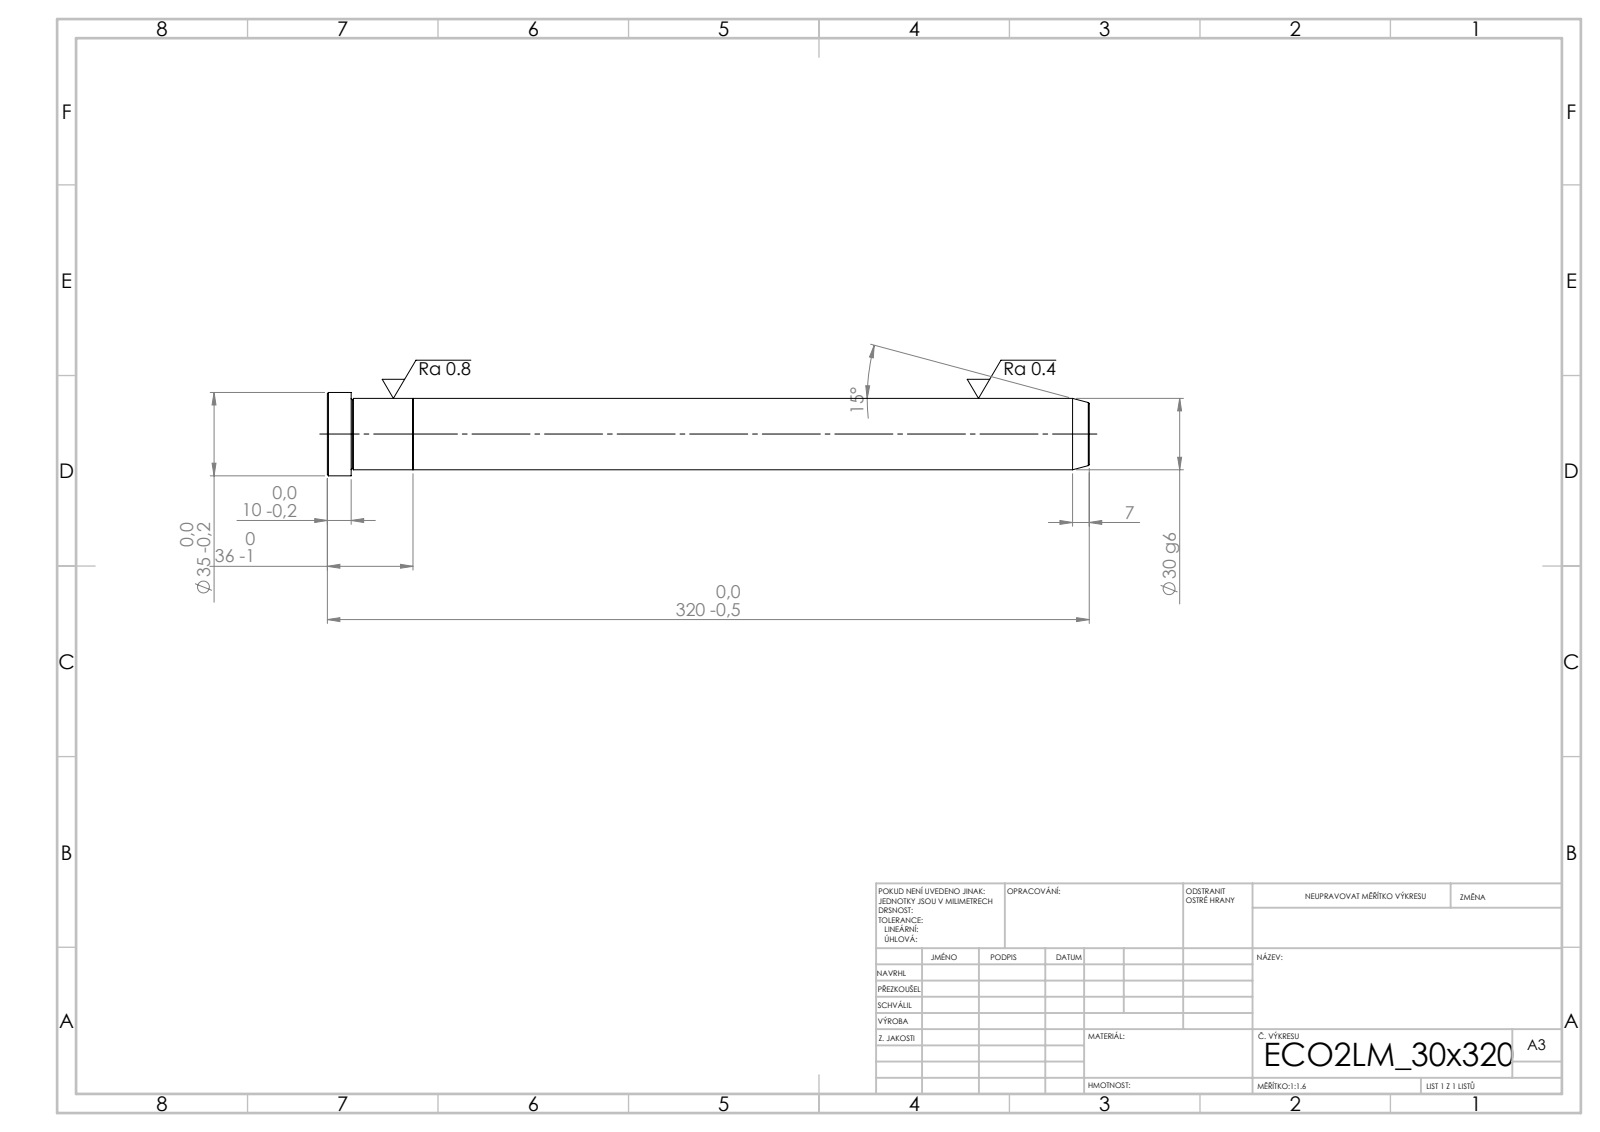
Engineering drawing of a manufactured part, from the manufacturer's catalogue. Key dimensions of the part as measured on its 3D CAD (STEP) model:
STEP written by: SolidWorks 2019 (CONFIG_CONTROL_DESIGN)
Units: millimetres
Bodies: 2 solids, 21 faces (5 planar, 6 cylindrical, 10 other)
Overall size (bounding box): 320 × 35 × 35
Volume: 228 102 mm³ · Surface area: 33 478 mm²
Round bosses / shafts (diameter × count): ⌀35 ×1, ⌀30 ×1
Main face-to-face distances: 36, 284, 320, 310, 26, 10
